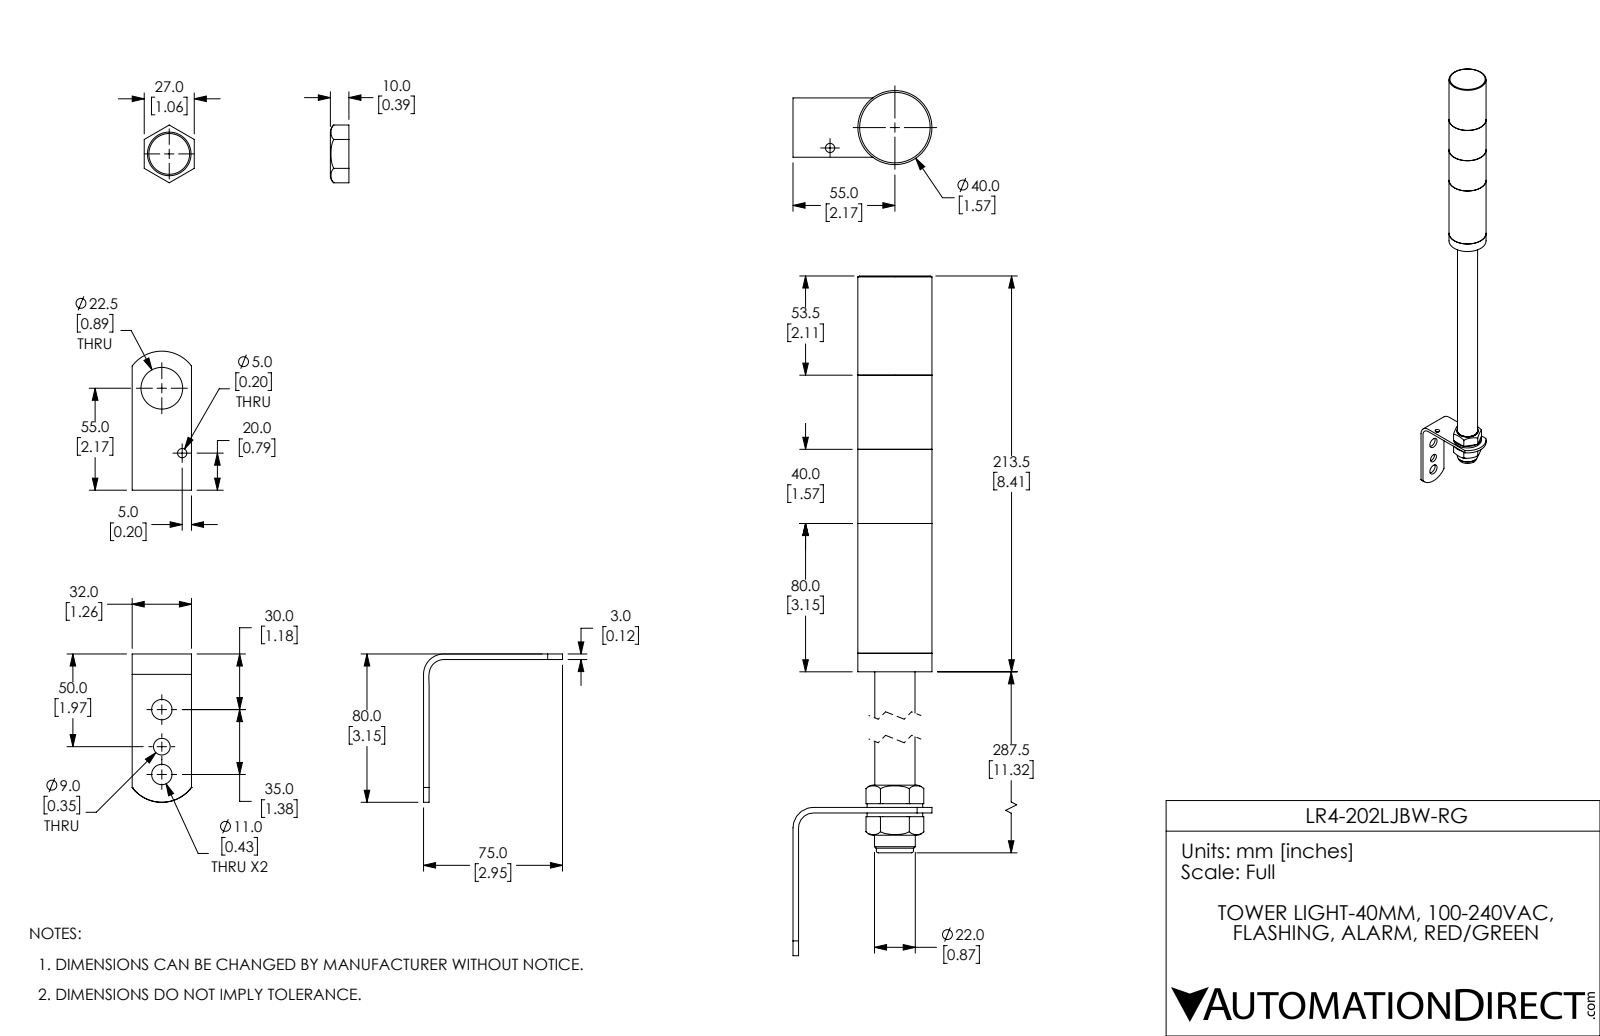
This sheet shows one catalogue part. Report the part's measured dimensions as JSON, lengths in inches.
{"part_name": "LR4-202LJBW-RG", "step_written_by": "SolidWorks 2017 (AUTOMOTIVE_DESIGN)", "units": "inches", "bodies": {"solids": 11, "faces": 143, "planar": 52, "cylindrical": 77, "other": 14}, "overall_size": [21.909, 2.953, 1.575], "volume_in3": 20.32, "surface_area_in2": 165.8, "round_holes": [[0.126, 2], [0.433, 2], [0.197, 1], [0.303, 1], [0.354, 1], [0.697, 1], [0.866, 1], [0.886, 1], [1.087, 1], [1.386, 1], [1.39, 1], [1.463, 1]], "round_bosses_or_shafts": [[1.575, 1], [1.461, 1], [1.366, 1], [1.181, 1], [0.854, 1]], "partial_cylinders_radius": [[0.787, 1]], "face_to_face_distances": [1.575, 3.15, 3.161, 3.276, 3.555, 4.85, 2.598, 4.173, 1.701, 0.197], "hole_center_spacings": [0.283, 0.567, 0.591, 0.787, 1.177, 1.378, 1.444, 1.717]}
